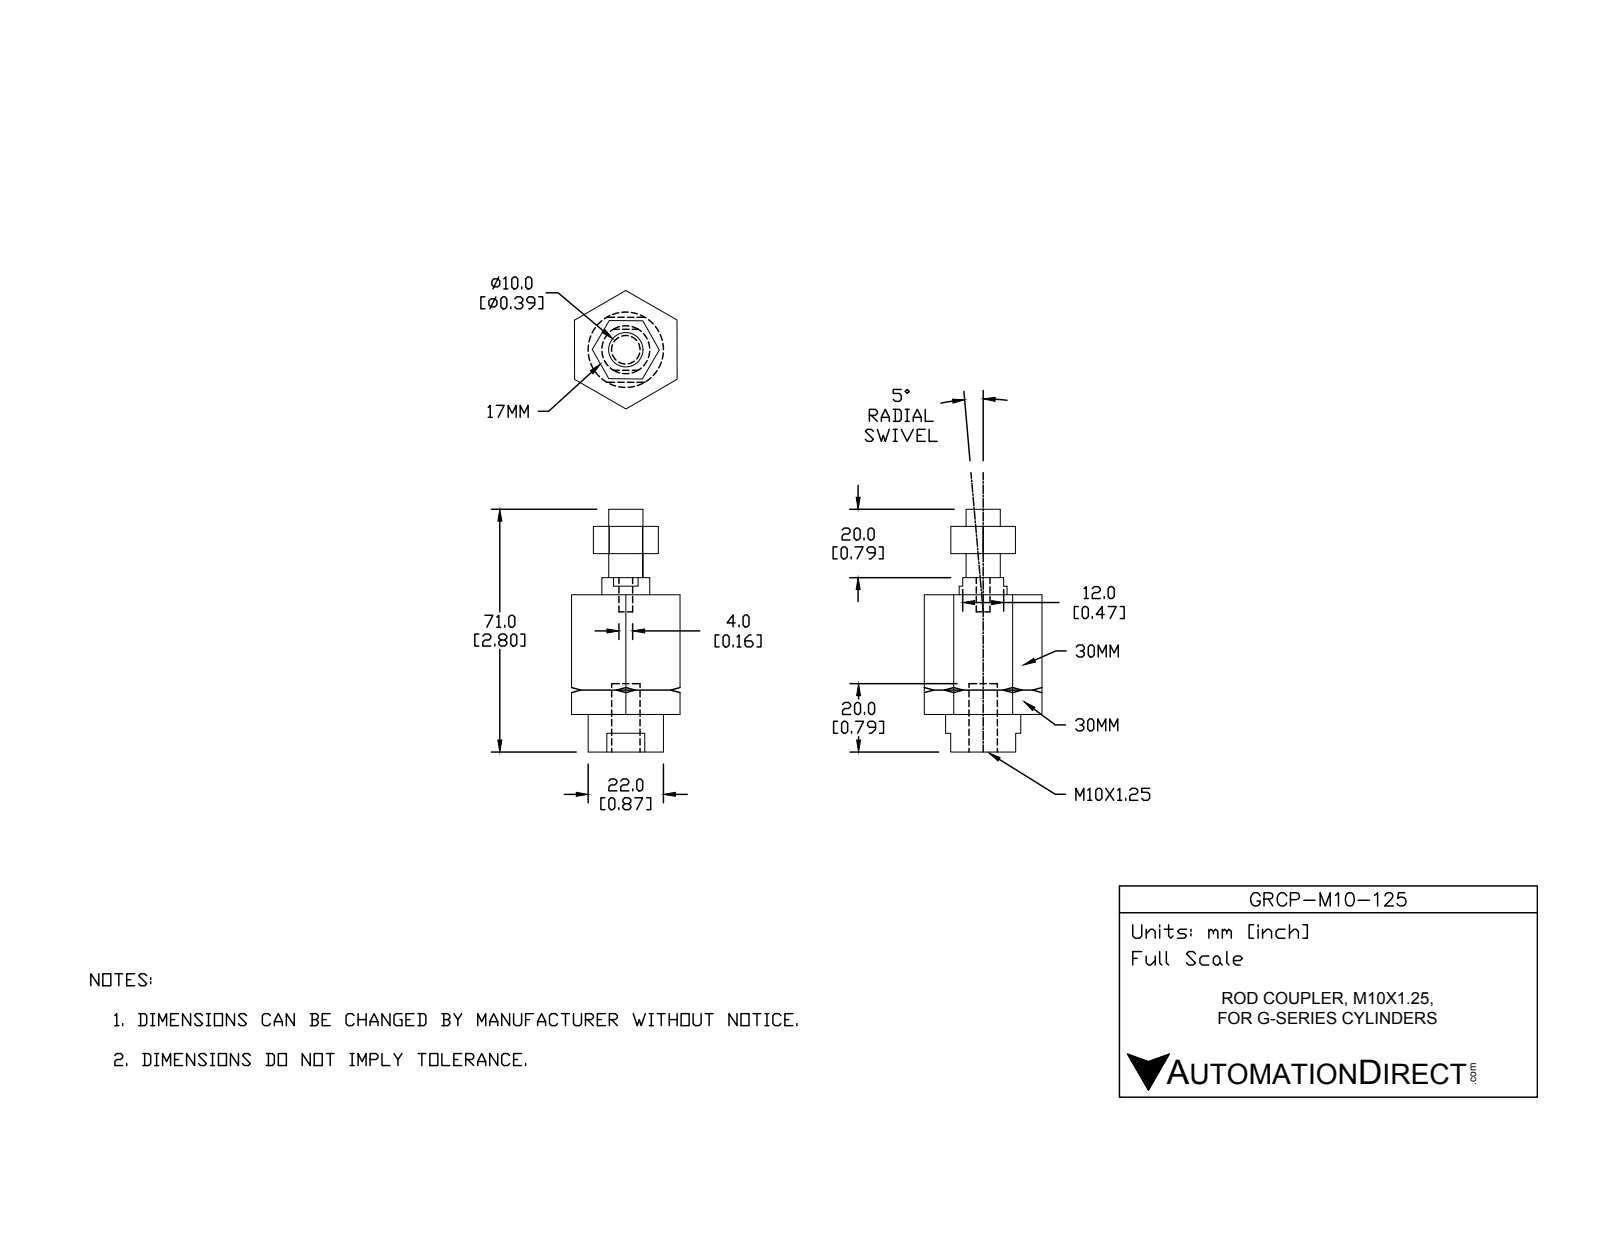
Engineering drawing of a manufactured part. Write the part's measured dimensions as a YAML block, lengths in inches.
part_name: "GRCP-M10-125"
step_written_by: "SolidWorks 2017 (AUTOMOTIVE_DESIGN)"
units: inches
bodies: {solids: 1, faces: 71, planar: 27, cylindrical: 10, other: 34}
overall_size: [2.795, 1.364, 1.181]
volume: 2.046
surface_area: 12.28
round_holes:
  - {diameter: 0.341, count: 1}
round_bosses_or_shafts:
  - {diameter: 0.866, count: 1}
  - {diameter: 0.551, count: 1}
  - {diameter: 0.394, count: 1}
face_to_face_distances: [1.181, 0.256, 0.925, 1.378, 1.811, 0.433, 0.669, 0.787, 0.217, 0.472]
